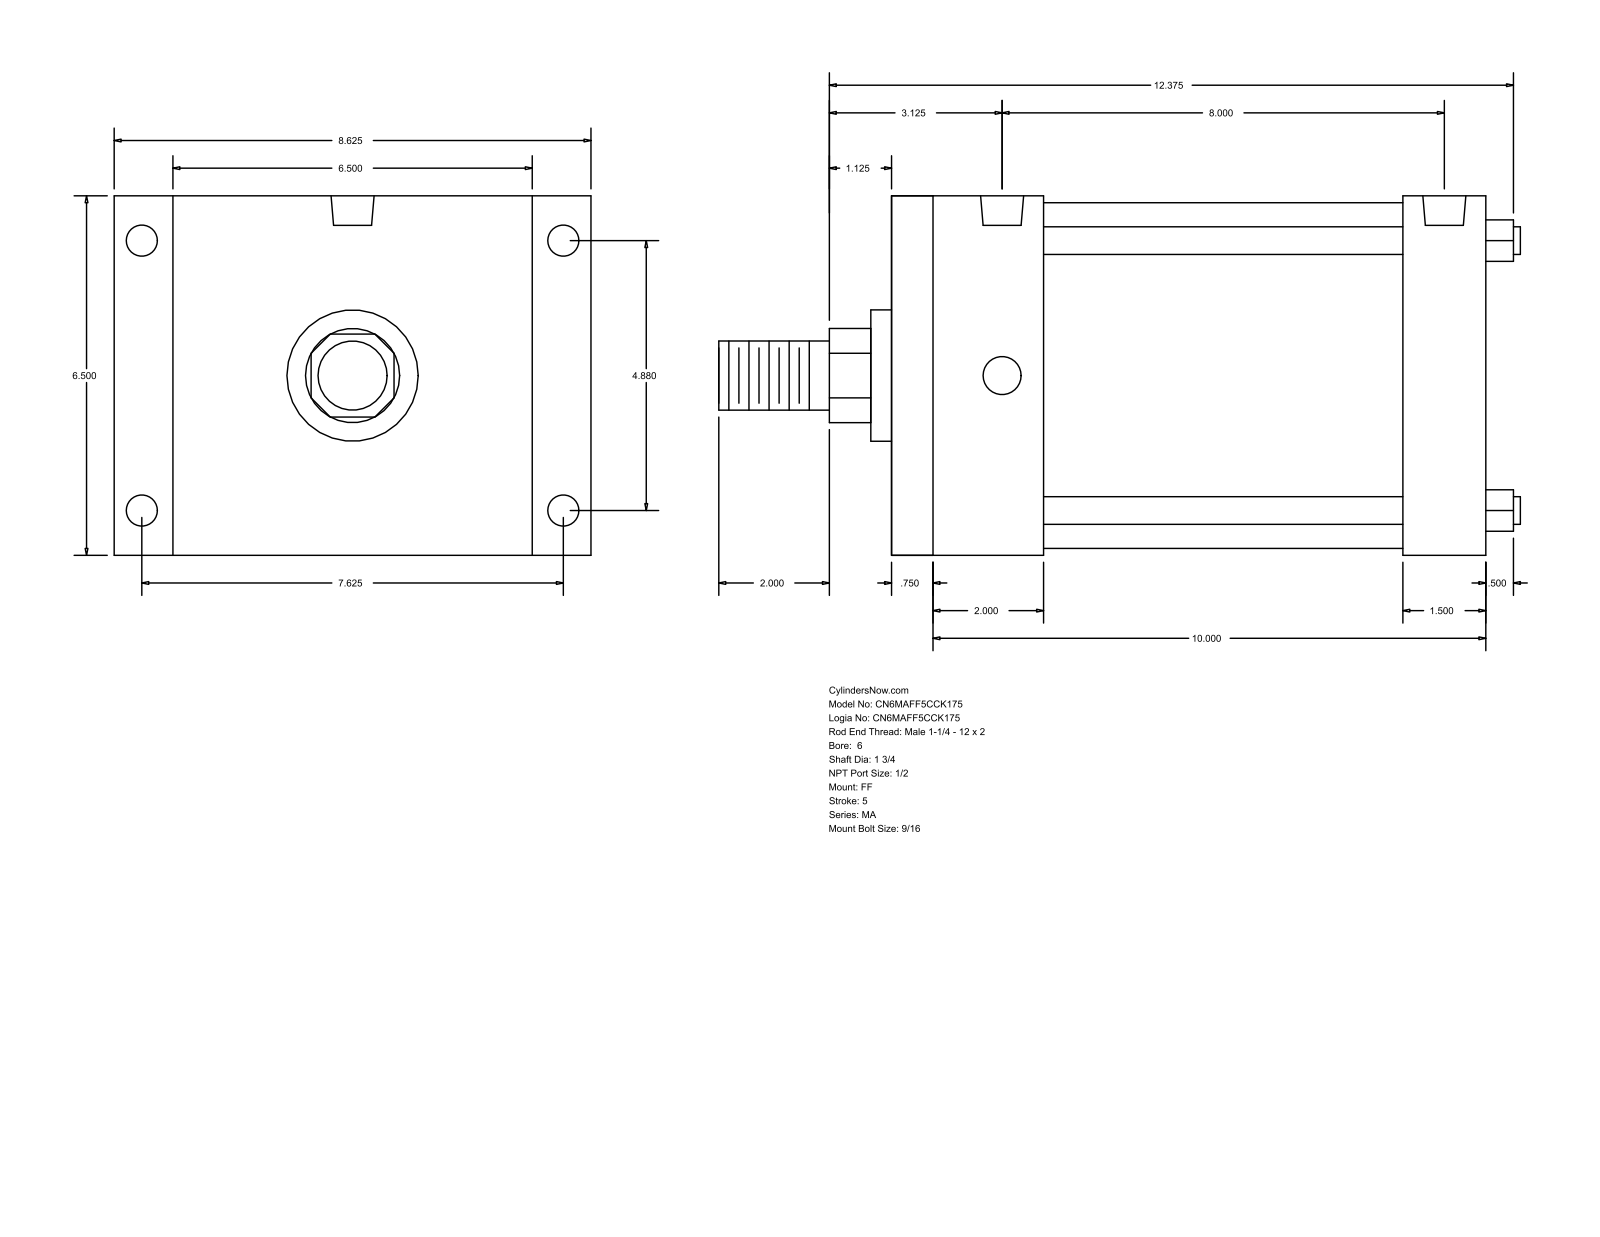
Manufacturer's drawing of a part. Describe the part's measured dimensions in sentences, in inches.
The part is named "MA_FF__0600_1.75". Its 3-D file was written by "GSSL Pune (CONFIG_CONTROL_DESIGN)". It is 0 solids with 92 faces: 64 planar, 28 cylindrical and 0 other. Overall it measures 14.5 by 8.625 by 6.5 inches. Round holes: 4 of diameter 0.563, 4 of diameter 0.687, 2 of diameter 0.778. Round bosses or shafts: 4 of diameter 0.5, 1 of diameter 6.25, 1 of diameter 2.375, 1 of diameter 1.75, 1 of diameter 1.25. Partial cylindrical surfaces (rounded edges, fillets, slot ends): 1 of radius 0.852. The main face-to-face distances are 6.5, 10.75, 0.75, 10, 2, 2.75, 8.5, 1.5, 8, 9.25. The hole center spacings are 4.88, 7.625, 8, 9.053.
